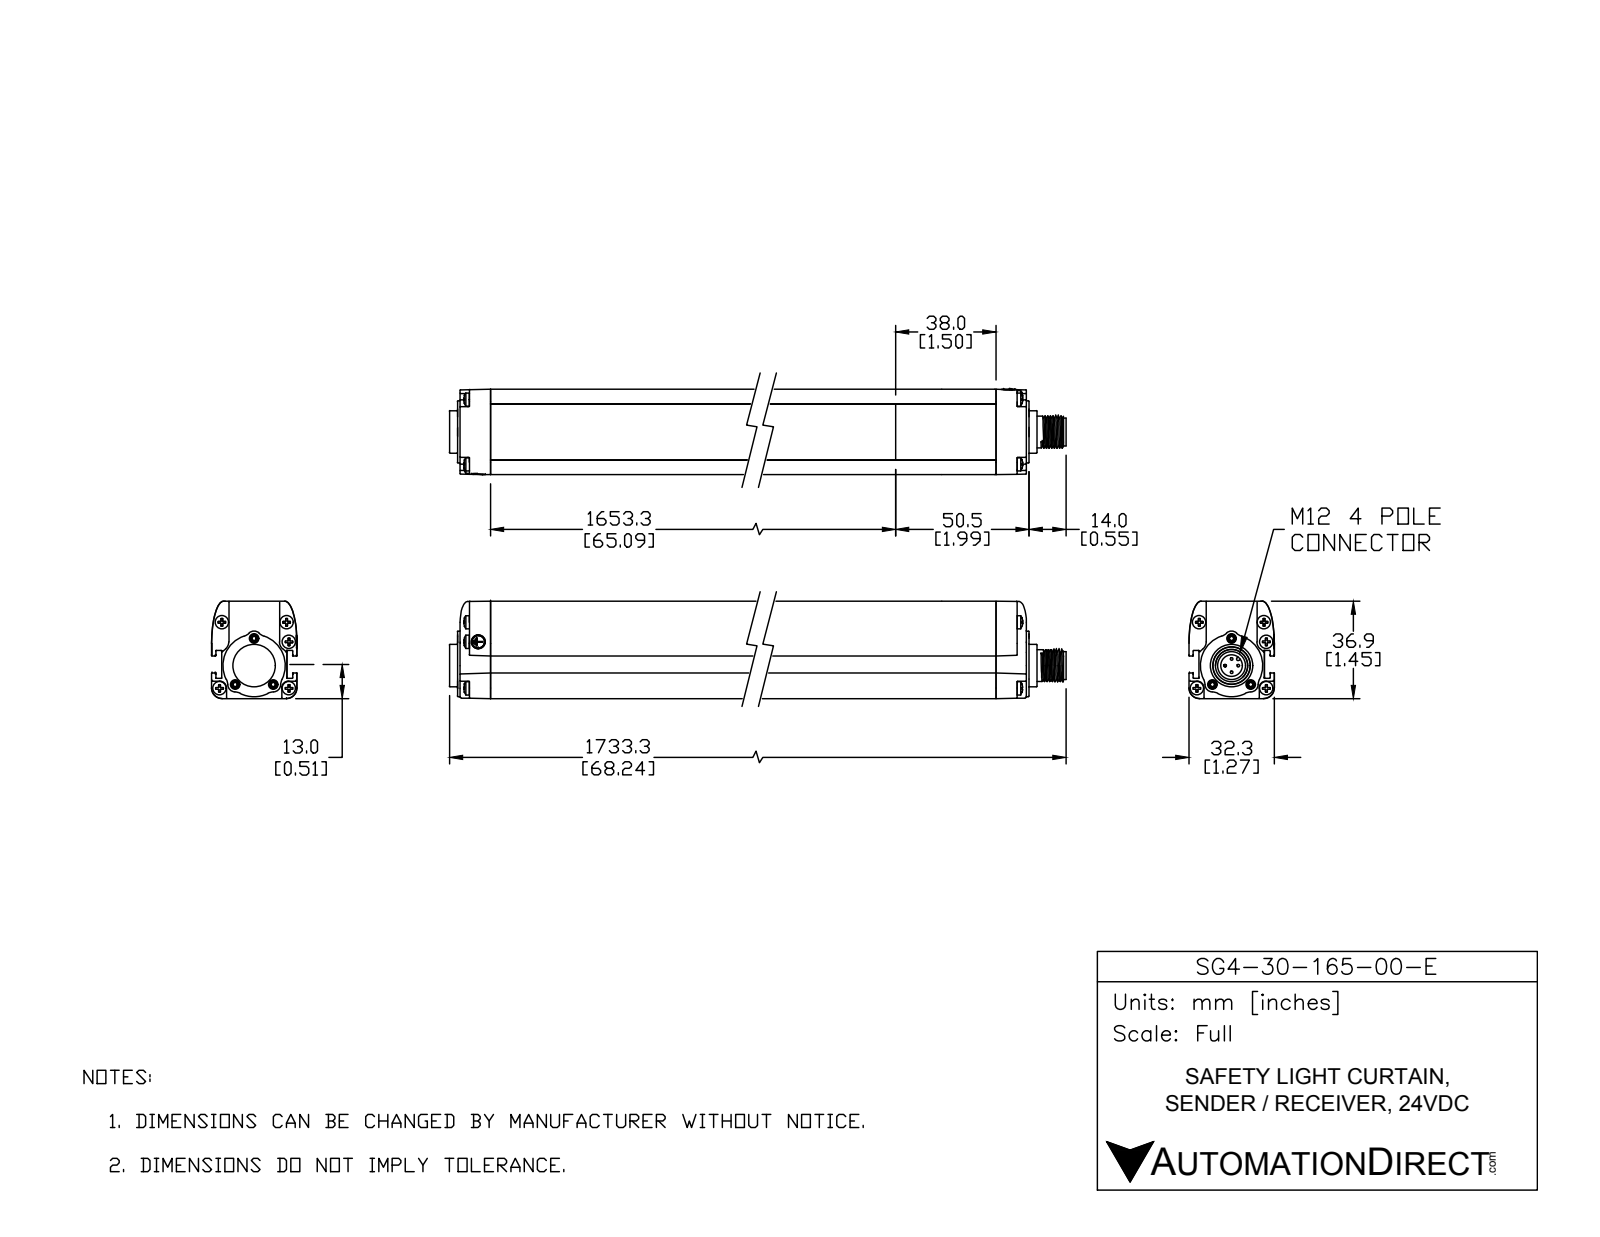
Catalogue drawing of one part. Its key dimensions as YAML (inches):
part_name: "SG4-30-165-OO-E"
step_written_by: "SolidWorks 2017 (AUTOMOTIVE_DESIGN)"
units: inches
bodies: {solids: 29, faces: 1674, planar: 410, cylindrical: 591, other: 673}
overall_size: [68.245, 2.48, 2.055]
volume: 108.9
surface_area: 645
round_holes:
  - {diameter: 0.106, count: 6}
  - {diameter: 0.209, count: 6}
  - {diameter: 0.081, count: 4}
  - {diameter: 0.165, count: 4}
  - {diameter: 0.26, count: 4}
  - {diameter: 0.059, count: 3}
  - {diameter: 0.142, count: 3}
  - {diameter: 0.323, count: 1}
  - {diameter: 0.376, count: 1}
  - {diameter: 0.433, count: 1}
  - {diameter: 0.563, count: 1}
round_bosses_or_shafts:
  - {diameter: 0.197, count: 10}
  - {diameter: 0.394, count: 4}
  - {diameter: 0.039, count: 4}
  - {diameter: 0.185, count: 2}
  - {diameter: 0.63, count: 1}
  - {diameter: 0.55, count: 1}
  - {diameter: 0.472, count: 1}
  - {diameter: 0.413, count: 1}
partial_cylinders:
  - {radius: 0.008, count: 148}
  - {radius: 0.004, count: 120}
  - {radius: 0.006, count: 18}
  - {radius: 0.106, count: 18}
  - {radius: 0.118, count: 8}
  - {radius: 0.197, count: 7}
  - {radius: 0.11, count: 3}
  - {radius: 0.016, count: 2}
face_to_face_distances: [0.079, 1.272, 1.429, 0.15, 1.122, 1.35, 0.157, 0.972, 0.333, 0.063]
hole_center_spacings: [0.569, 65.017, 0.402, 0.24, 0.293, 0.52, 0.541, 0.619]
